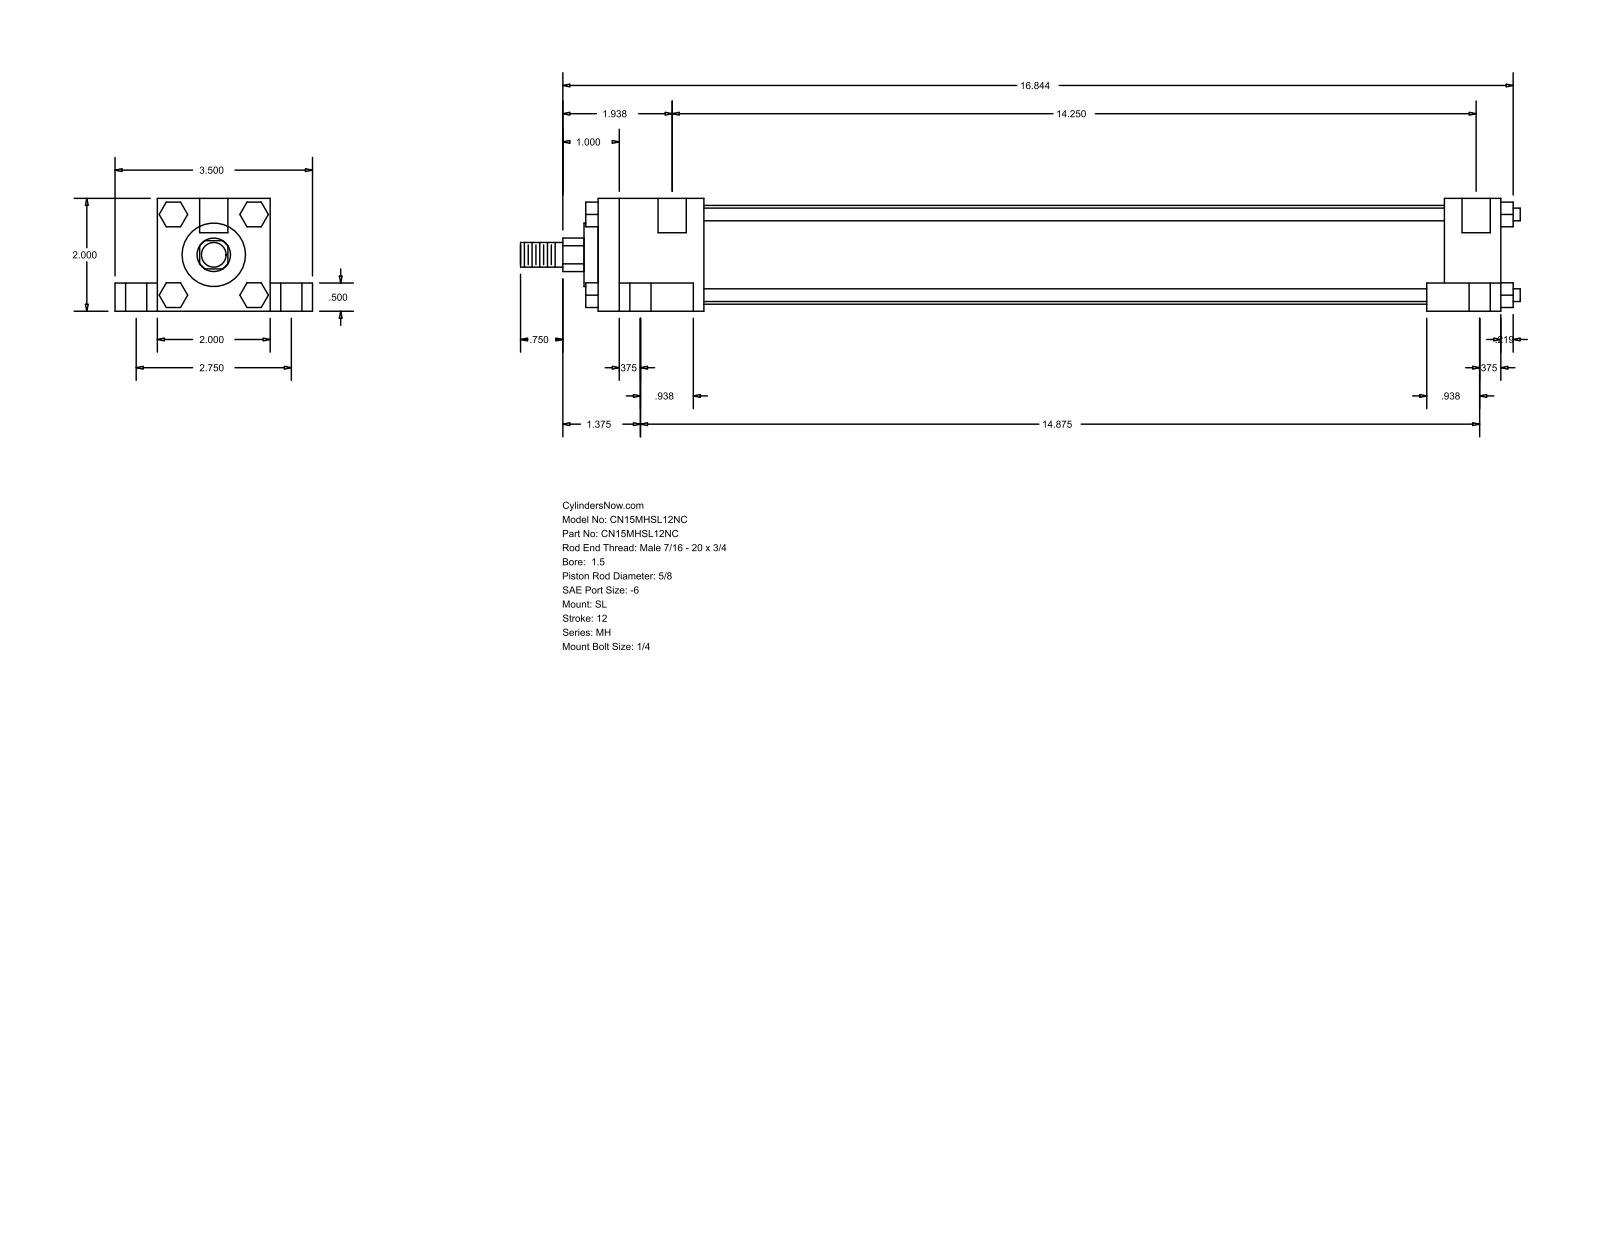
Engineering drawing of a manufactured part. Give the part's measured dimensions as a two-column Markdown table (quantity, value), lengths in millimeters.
| quantity | value |
| --- | --- |
| part name | MH_SL__0150_0.625 |
| STEP written by | GSSL Pune (CONFIG_CONTROL_DESIGN) |
| units | millimeters |
| bodies | 0 solids, 148 faces (112 planar, 36 cylindrical, 0 other) |
| overall size | 450.06 × 88.9 × 50.8 |
| round holes (diameter × count) | 5.56 × 4, 9.53 × 4, 15.88 × 4, 12.7 × 2 |
| round bosses / shafts (diameter × count) | 5.71 × 4, 44.45 × 1, 28.57 × 1, 15.88 × 1, 11.11 × 1 |
| partial cylindrical surfaces (radius × count) | 7.54 × 1 |
| main face-to-face distances | 50.8, 38.1, 19.05, 12.7, 69.85, 406.39, 9.52, 381, 25.39, 47.62 |
| hole center spacings | 34.96, 36.65, 37.73, 69.84, 365.12, 365.21, 368.37, 377.83 |
